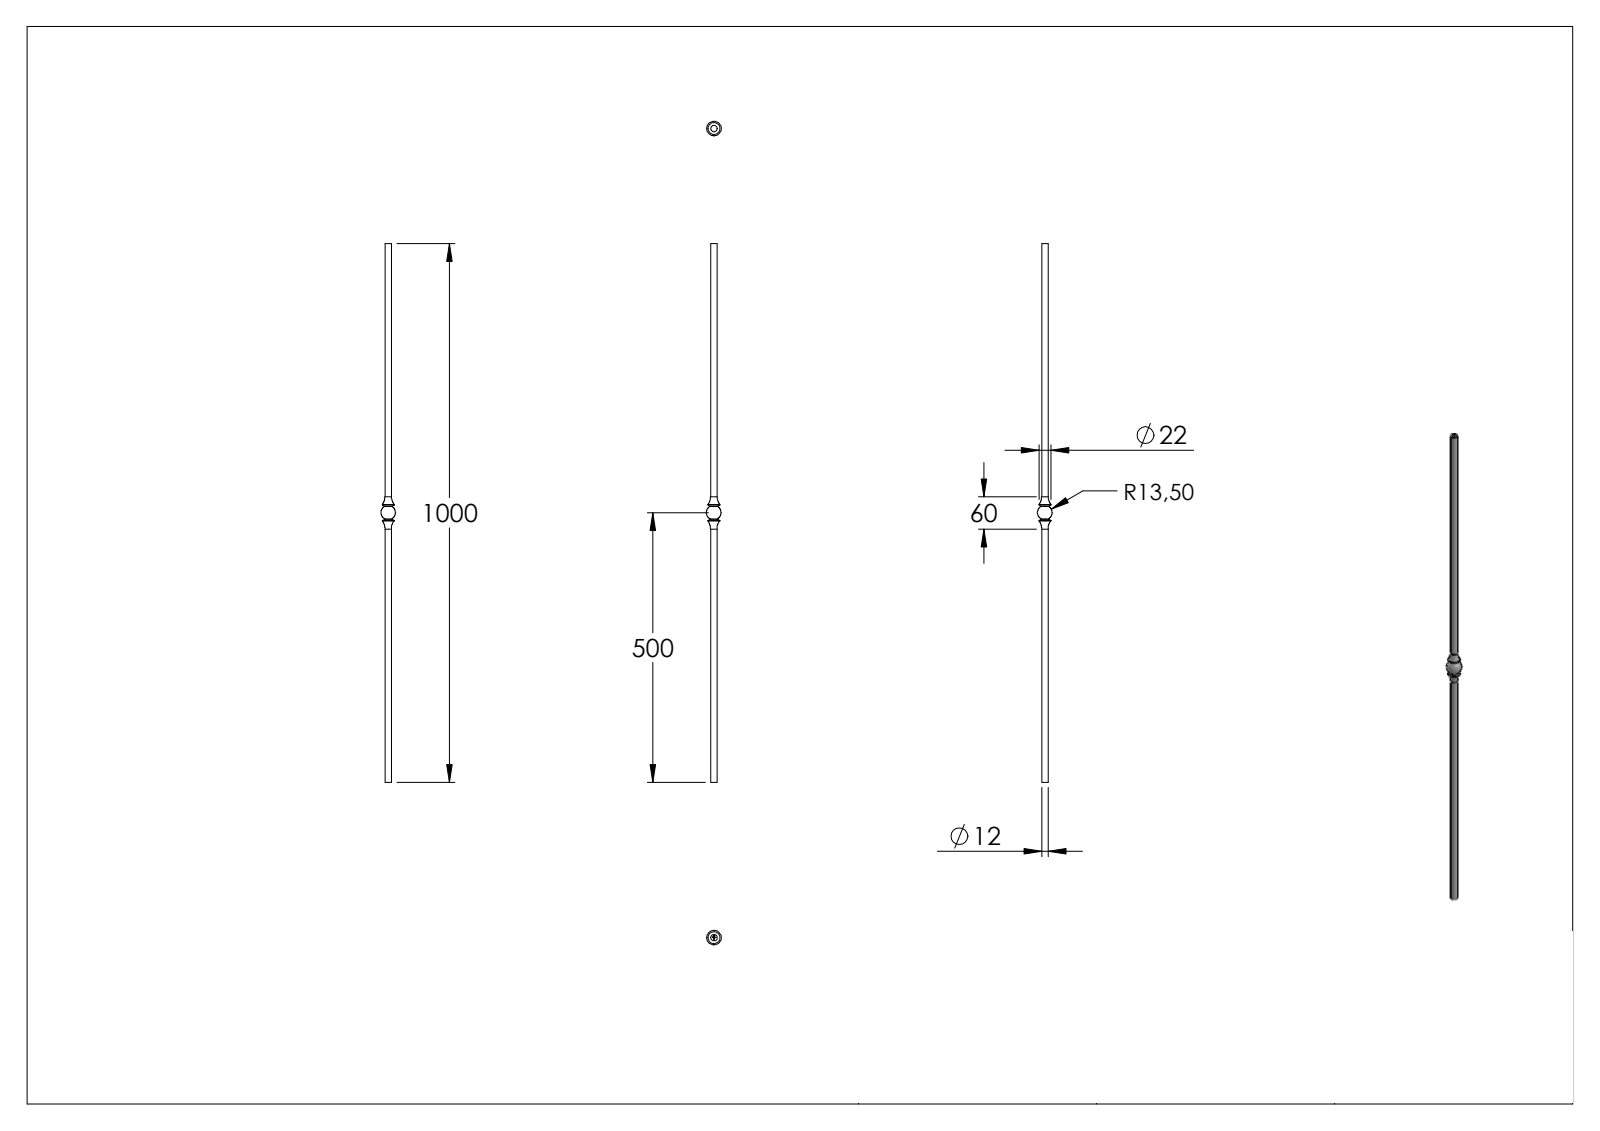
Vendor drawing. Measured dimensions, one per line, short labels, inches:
name: 1310
written by: SolidWorks 2018 (CONFIG_CONTROL_DESIGN)
unit: in
bodies: 1 solid, 212 faces (110 planar, 6 cylindrical, 96 other)
size: 39.37 × 1.063 × 1.063
volume: 7.546 in³; area: 61.82 in²
bosses: 1× ⌀0.866, 1× ⌀0.512, 1× ⌀0.472
face distances: 39.37, 39.366, 0.013, 0.064, 0.087, 0.05, 0.027, 0.096, 0.013, 0.114
